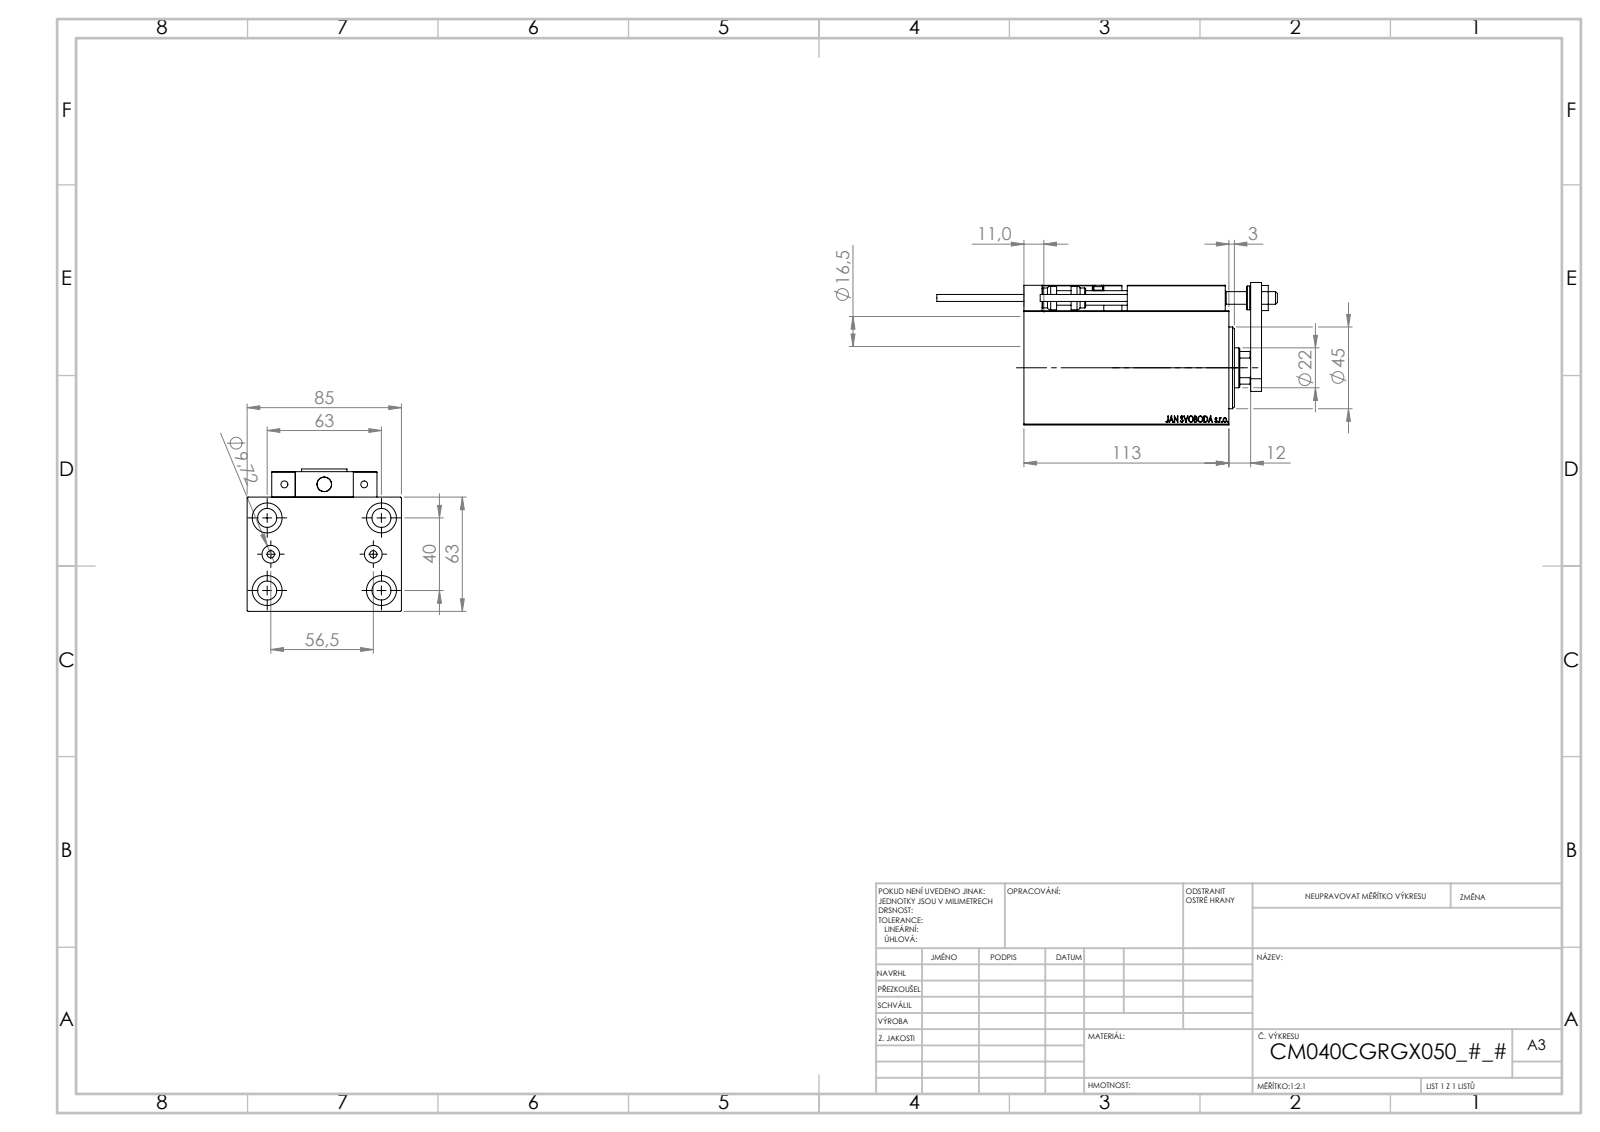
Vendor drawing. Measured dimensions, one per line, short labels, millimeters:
name: ALLEN BOLT D5; ALLEN BOLT D8; KONCOVKA; NUT_D12 (+7 more)
written by: SolidWorks 2019 (CONFIG_CONTROL_DESIGN)
unit: mm
bodies: 23 solids, 1278 faces (560 planar, 184 cylindrical, 534 other)
size: 187.7 × 85 × 78.5
volume: 561 785 mm³; area: 119 821 mm²
holes: 6× ⌀4, 5× ⌀8, 5× ⌀16.5, 4× ⌀3.2, 4× ⌀10.5, 2× ⌀5, 2× ⌀9.72, 1× ⌀7, 1× ⌀12.5, 1× ⌀22, 1× ⌀25.5, 1× ⌀40
bosses: 2× ⌀5, 2× ⌀3.8, 1× ⌀13, 1× ⌀11
rounds: 30× R0.3, 2× R3, 1× R10.5
face distances: 63, 85, 12, 101, 113, 14, 77, 6, 15, 18
hole spacings: 37.31, 11.37, 20, 20.1, 20.5, 29.59, 29.69, 36.06
